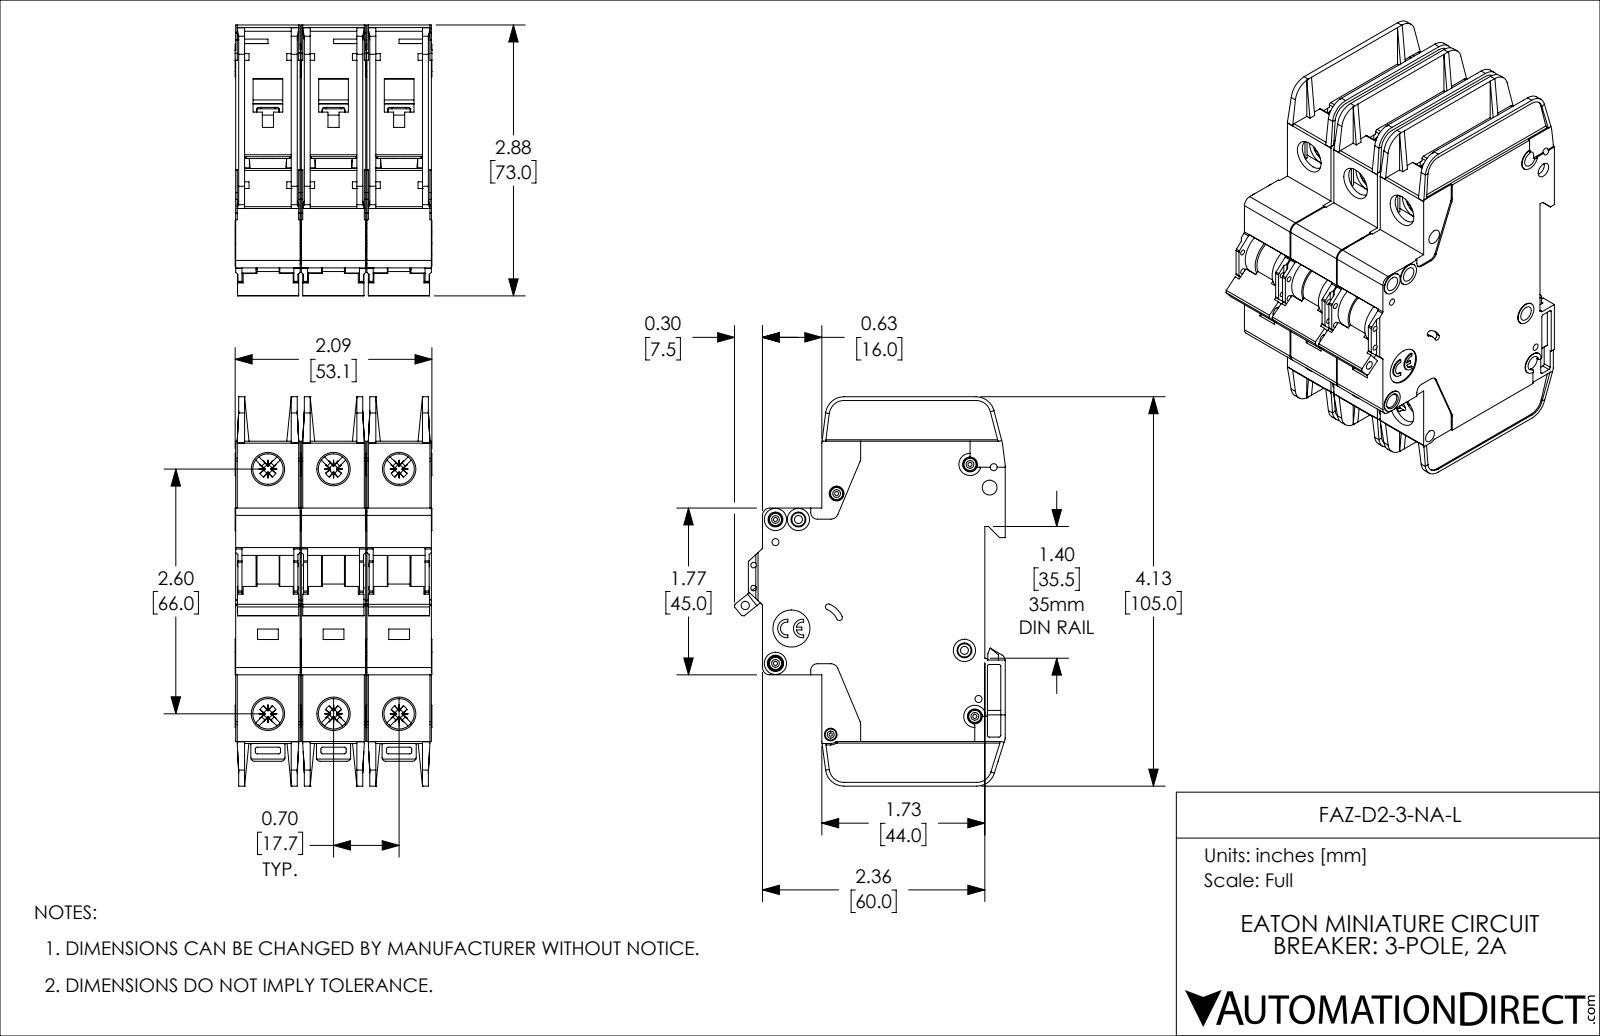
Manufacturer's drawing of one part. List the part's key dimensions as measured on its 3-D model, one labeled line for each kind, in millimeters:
Part name (STEP PRODUCT): FAZ-D2-3-NA-L
STEP written by: SolidWorks 2019 (AUTOMOTIVE_DESIGN)
Units: millimetres
Bodies: 3 solids, 3381 faces (2013 planar, 1071 cylindrical, 297 other)
Overall size (bounding box): 105 × 73.1 × 53.1
Volume: 230 200 mm³ · Surface area: 79 350 mm²
Round holes (diameter × count): ⌀4 ×8, ⌀8.2 ×6, ⌀1.1 ×5, ⌀1.9 ×4, ⌀1.5 ×2, ⌀2.2 ×2, ⌀0.9 ×1, ⌀2.3 ×1, ⌀2.5 ×1, ⌀3.4 ×1, ⌀10 ×1
Round bosses / shafts (diameter × count): ⌀3.3 ×5, ⌀6 ×4, ⌀3 ×4, ⌀2.5 ×3
Partial cylindrical surfaces — rounded edges, fillets, slot ends (radius × count): R0.5 ×72, R0.4 ×30, R1 ×18, R1.1 ×12, R2 ×12, R0.2 ×6, R0.3 ×6, R0.7 ×6
Main face-to-face distances: 17.7, 1.2, 35.4, 17.4, 15, 35.1, 18.9, 16.5, 2.7, 2.4
Hole centre spacings: 17.7, 68.3, 66, 6.2, 13.6, 22.1, 35.4, 74.9
